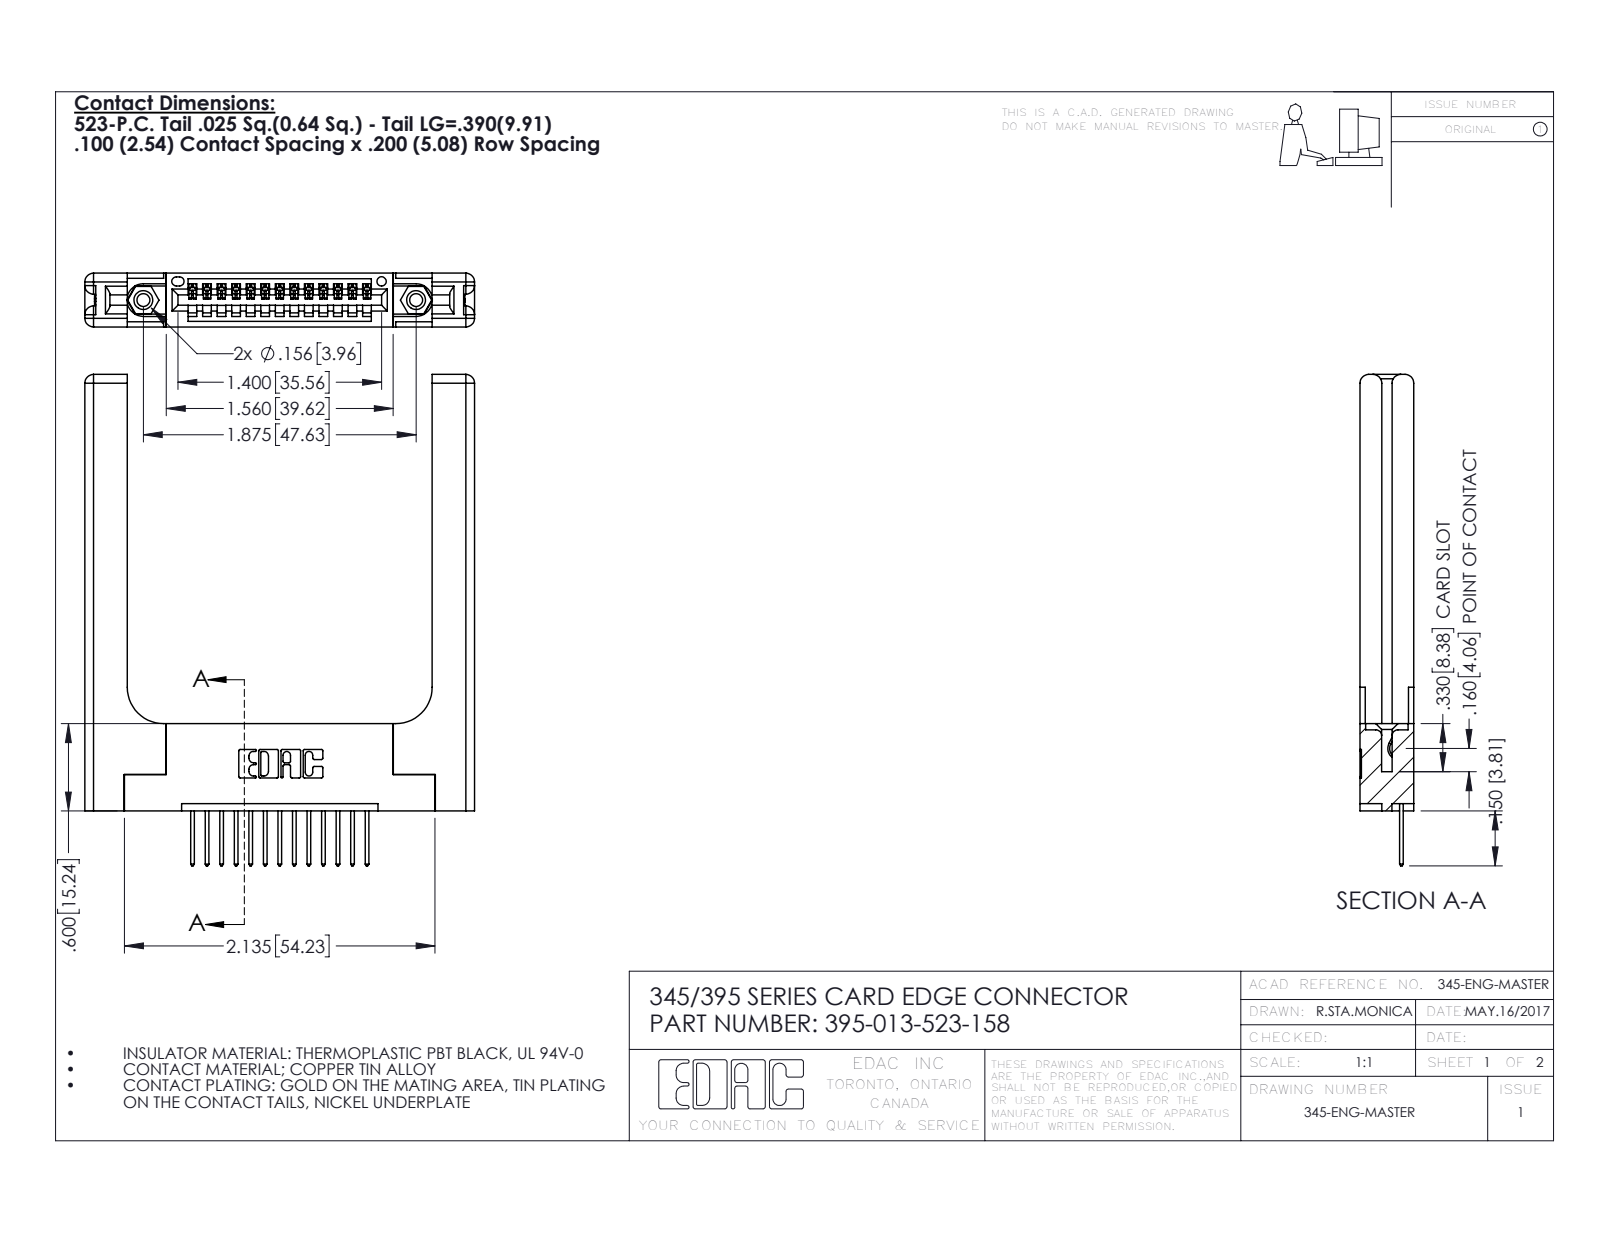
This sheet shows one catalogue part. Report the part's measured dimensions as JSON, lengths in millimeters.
{"part_name": "345-250-001_345-250-001-102; 345 Part_Flush Mounting Lugs - 0.156 Dia-TH; 345-220-058_345-220-058; 345-292-001_345-293-123 (+1 more)", "step_written_by": "SolidWorks 2016 (CONFIG_CONTROL_DESIGN)", "units": "millimeters", "bodies": {"solids": 18, "faces": 1136, "planar": 748, "cylindrical": 328, "other": 60}, "overall_size": [85.8, 68, 9.4], "volume_mm3": 14700, "surface_area_mm2": 13190, "round_holes": [[2.3, 2], [3.2, 2], [4, 2], [1.6, 1]], "round_bosses_or_shafts": [[3.9, 2]], "partial_cylinders_radius": [[0.2, 26], [0.3, 26], [0.3, 22], [1.5, 16], [0.2, 6], [0.8, 6], [0.7, 3], [0.8, 2]], "face_to_face_distances": [9.4, 1.8, 7.6, 3.8, 2, 3.8, 5.6, 5.1, 53.2, 2.5], "hole_center_spacings": [6.9, 41.7, 47.6]}
